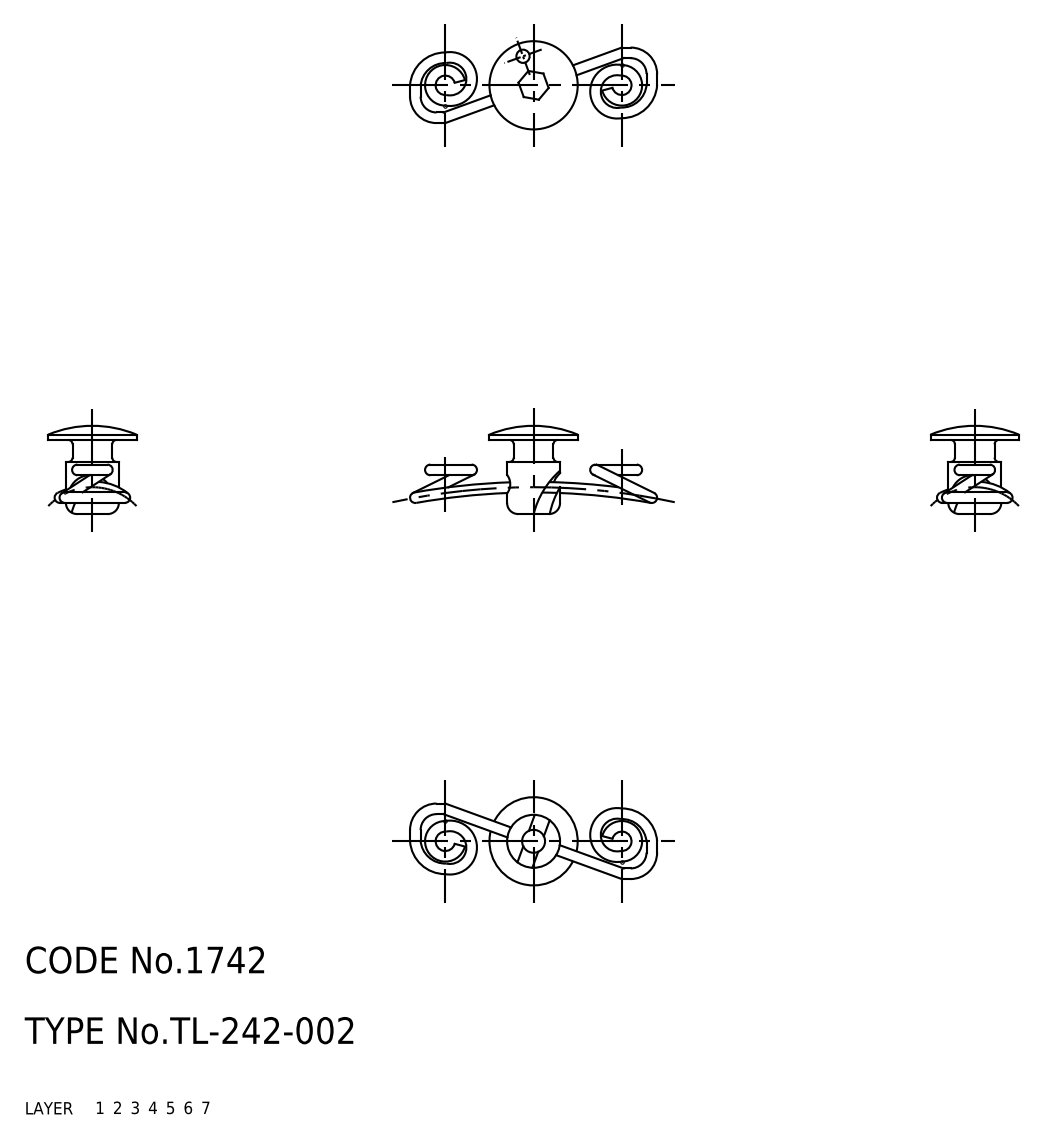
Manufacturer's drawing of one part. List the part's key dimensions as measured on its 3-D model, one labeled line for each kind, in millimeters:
Part name (STEP PRODUCT): fastener; spring; TL_242_002_31155_36
STEP written by: CADfix (AUTOMOTIVE_DESIGN)
Units: millimetres
Bodies: 2 solids, 63 faces (0 planar, 0 cylindrical, 63 other)
Overall size (bounding box): 28.03 × 10 × 9.91
Volume: 289 mm³ · Surface area: 689 mm²
